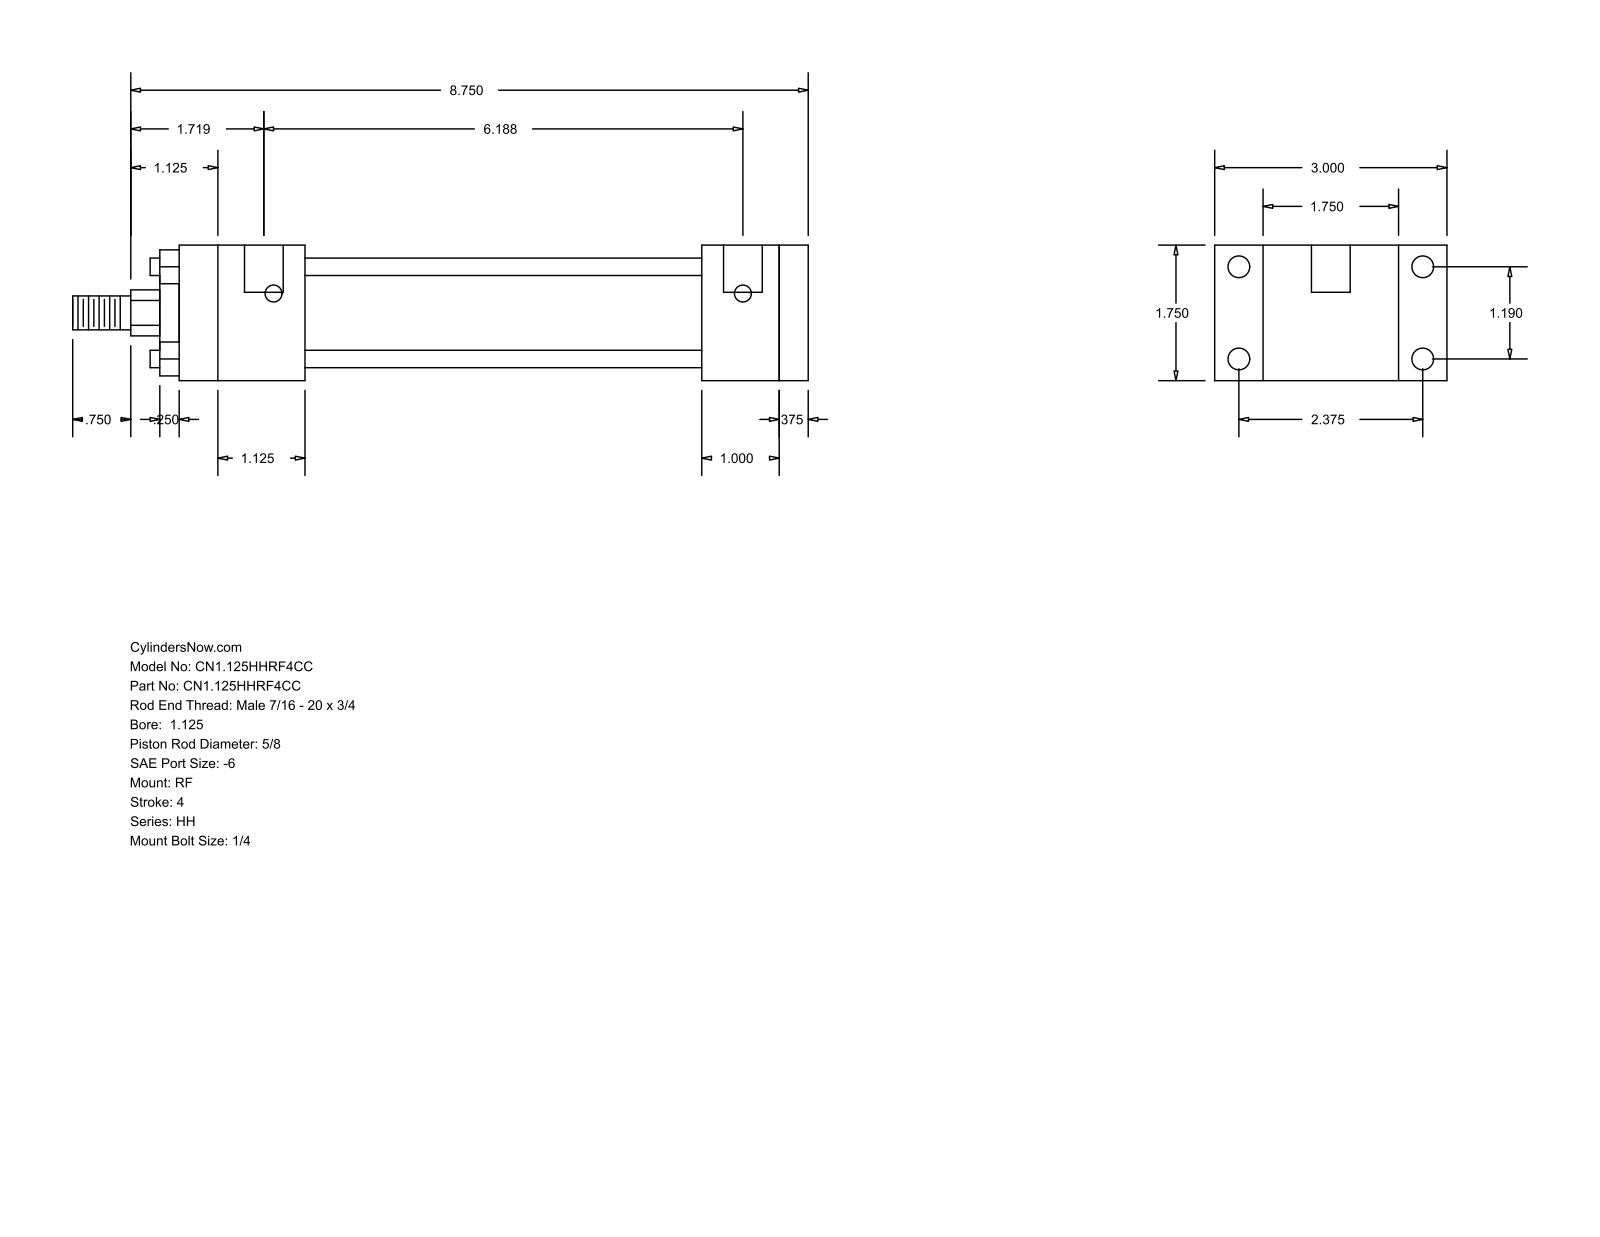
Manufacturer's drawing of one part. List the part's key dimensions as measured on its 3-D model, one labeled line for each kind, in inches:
Part name (STEP PRODUCT): HH_RF__0112_0.625
STEP written by: GSSL Pune (CONFIG_CONTROL_DESIGN)
Units: inches
Bodies: 0 solids, 92 faces (64 planar, 28 cylindrical, 0 other)
Overall size (bounding box): 9.5 × 3 × 1.75
Round holes (diameter × count): ⌀0.219 ×4, ⌀0.281 ×4, ⌀0.5 ×2
Round bosses / shafts (diameter × count): ⌀0.225 ×4, ⌀1.375 ×1, ⌀1.125 ×1, ⌀0.625 ×1, ⌀0.437 ×1
Partial cylindrical surfaces — rounded edges, fillets, slot ends (radius × count): R0.297 ×1
Main face-to-face distances: 1.75, 0.375, 8.125, 1, 1.375, 0.625, 6.125, 6.5, 5.125, 1.625
Hole centre spacings: 1.19, 2.375, 2.656, 6.063, 0.125, 6.187
